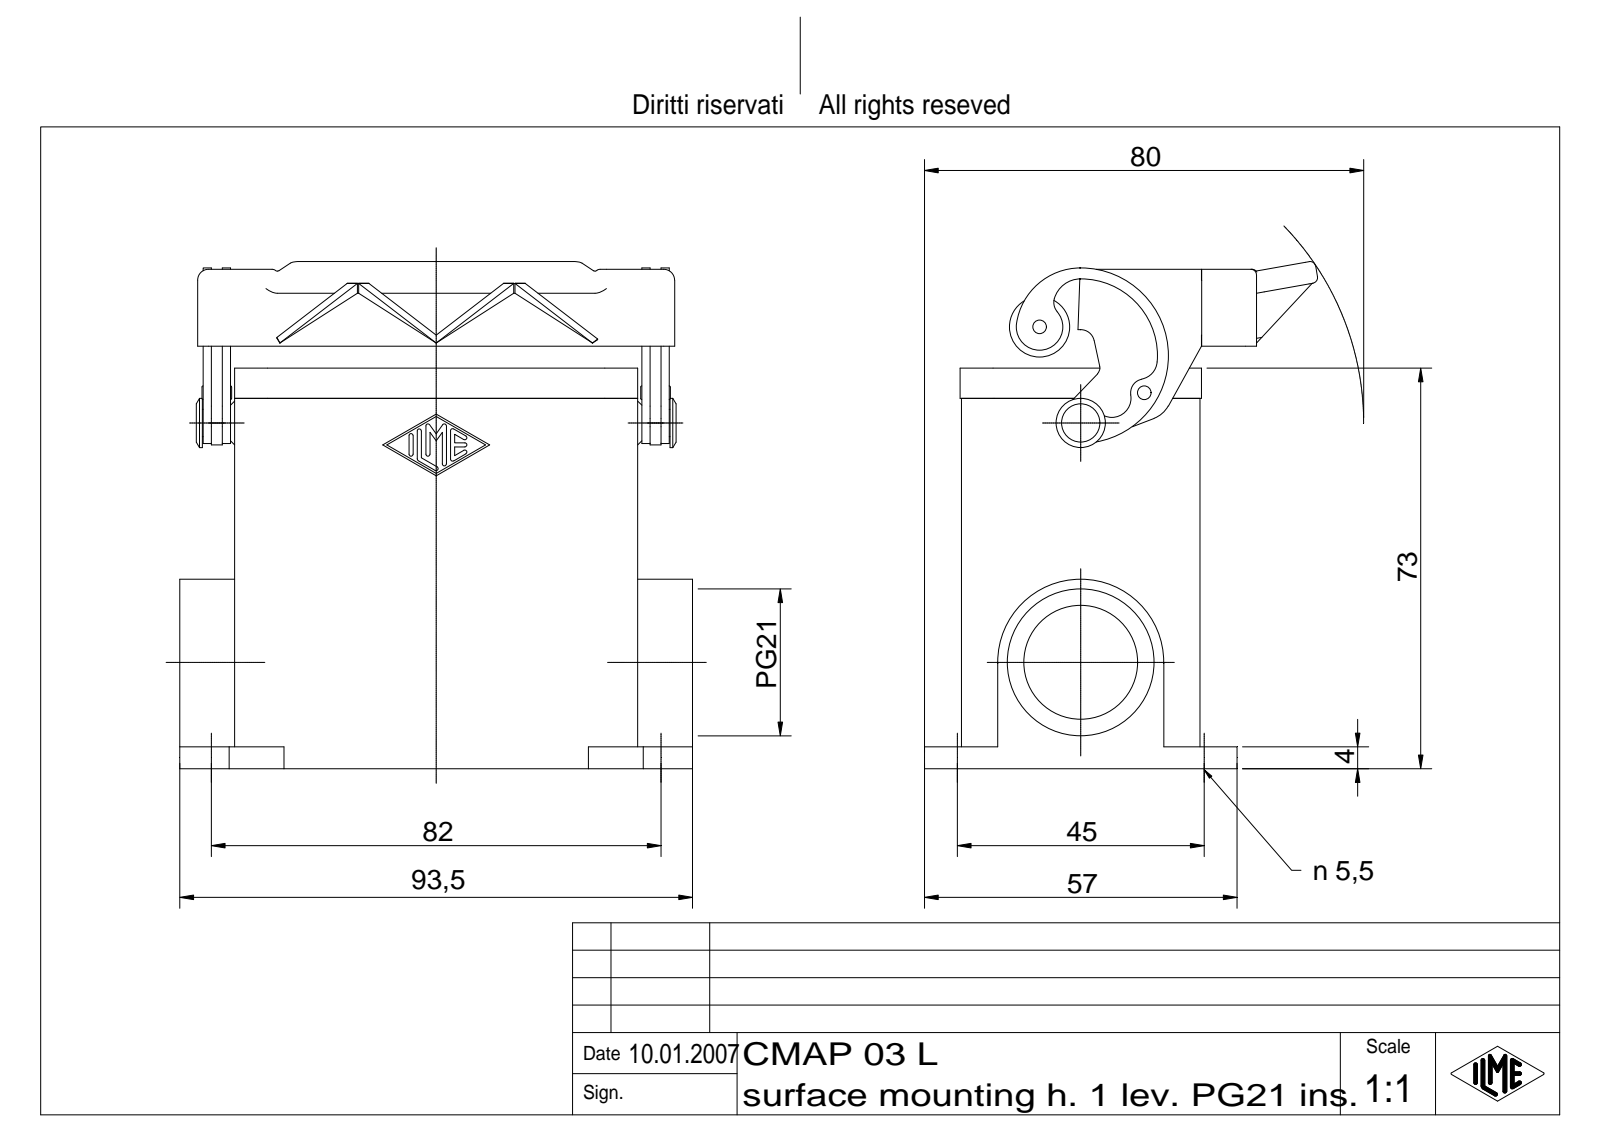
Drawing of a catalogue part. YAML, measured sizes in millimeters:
part_name: "CMAP 03 L"
step_written_by: "Autodesk Inventor 7 (AUTOMOTIVE_DESIGN)"
units: millimeters
bodies: {solids: 4, faces: 432, planar: 164, cylindrical: 123, other: 145}
overall_size: [93.5, 92.42, 71.7]
volume: 103913
surface_area: 54169
round_holes:
  - {diameter: 5.5, count: 4}
  - {diameter: 2, count: 1}
  - {diameter: 20.78, count: 1}
  - {diameter: 26.78, count: 1}
round_bosses_or_shafts:
  - {diameter: 11, count: 1}
  - {diameter: 9, count: 1}
  - {diameter: 5, count: 1}
  - {diameter: 3, count: 1}
  - {diameter: 2.5, count: 1}
partial_cylinders:
  - {radius: 0.38, count: 14}
  - {radius: 2, count: 12}
  - {radius: 6, count: 8}
  - {radius: 1, count: 7}
  - {radius: 1.5, count: 5}
  - {radius: 3, count: 4}
  - {radius: 2.5, count: 3}
  - {radius: 3.5, count: 2}
face_to_face_distances: [3, 40.5, 4, 43.5, 37.5, 11.75, 67.5, 61.75, 8.75, 63.5]
hole_center_spacings: [45, 82, 93.54, 50.46]
